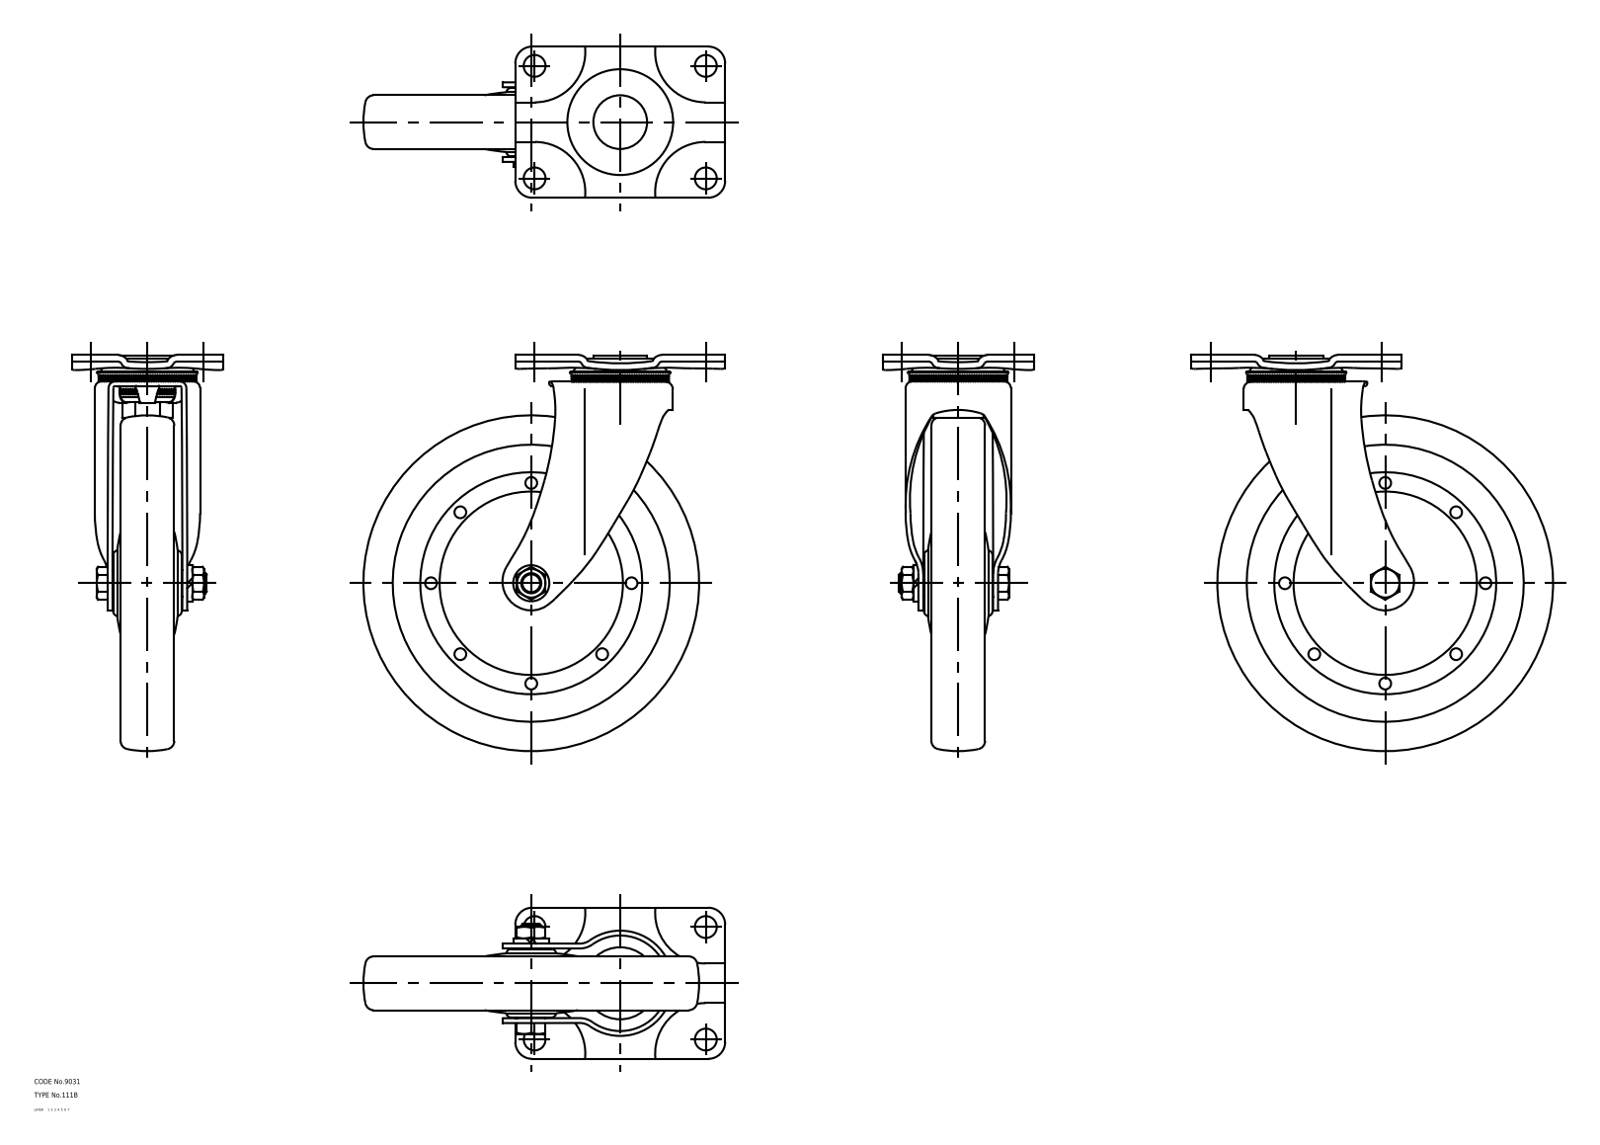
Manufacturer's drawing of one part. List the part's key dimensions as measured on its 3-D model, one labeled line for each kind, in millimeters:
Part name (STEP PRODUCT): 67143177; 67143190; 67143203; 67143216 (+1 more)
STEP written by: CADfix (AUTOMOTIVE_DESIGN)
Units: millimetres
Bodies: 5 solids, 454 faces (0 planar, 0 cylindrical, 454 other)
Overall size (bounding box): 236 × 215.5 × 90
Volume: 992 316 mm³ · Surface area: 158 951 mm²
